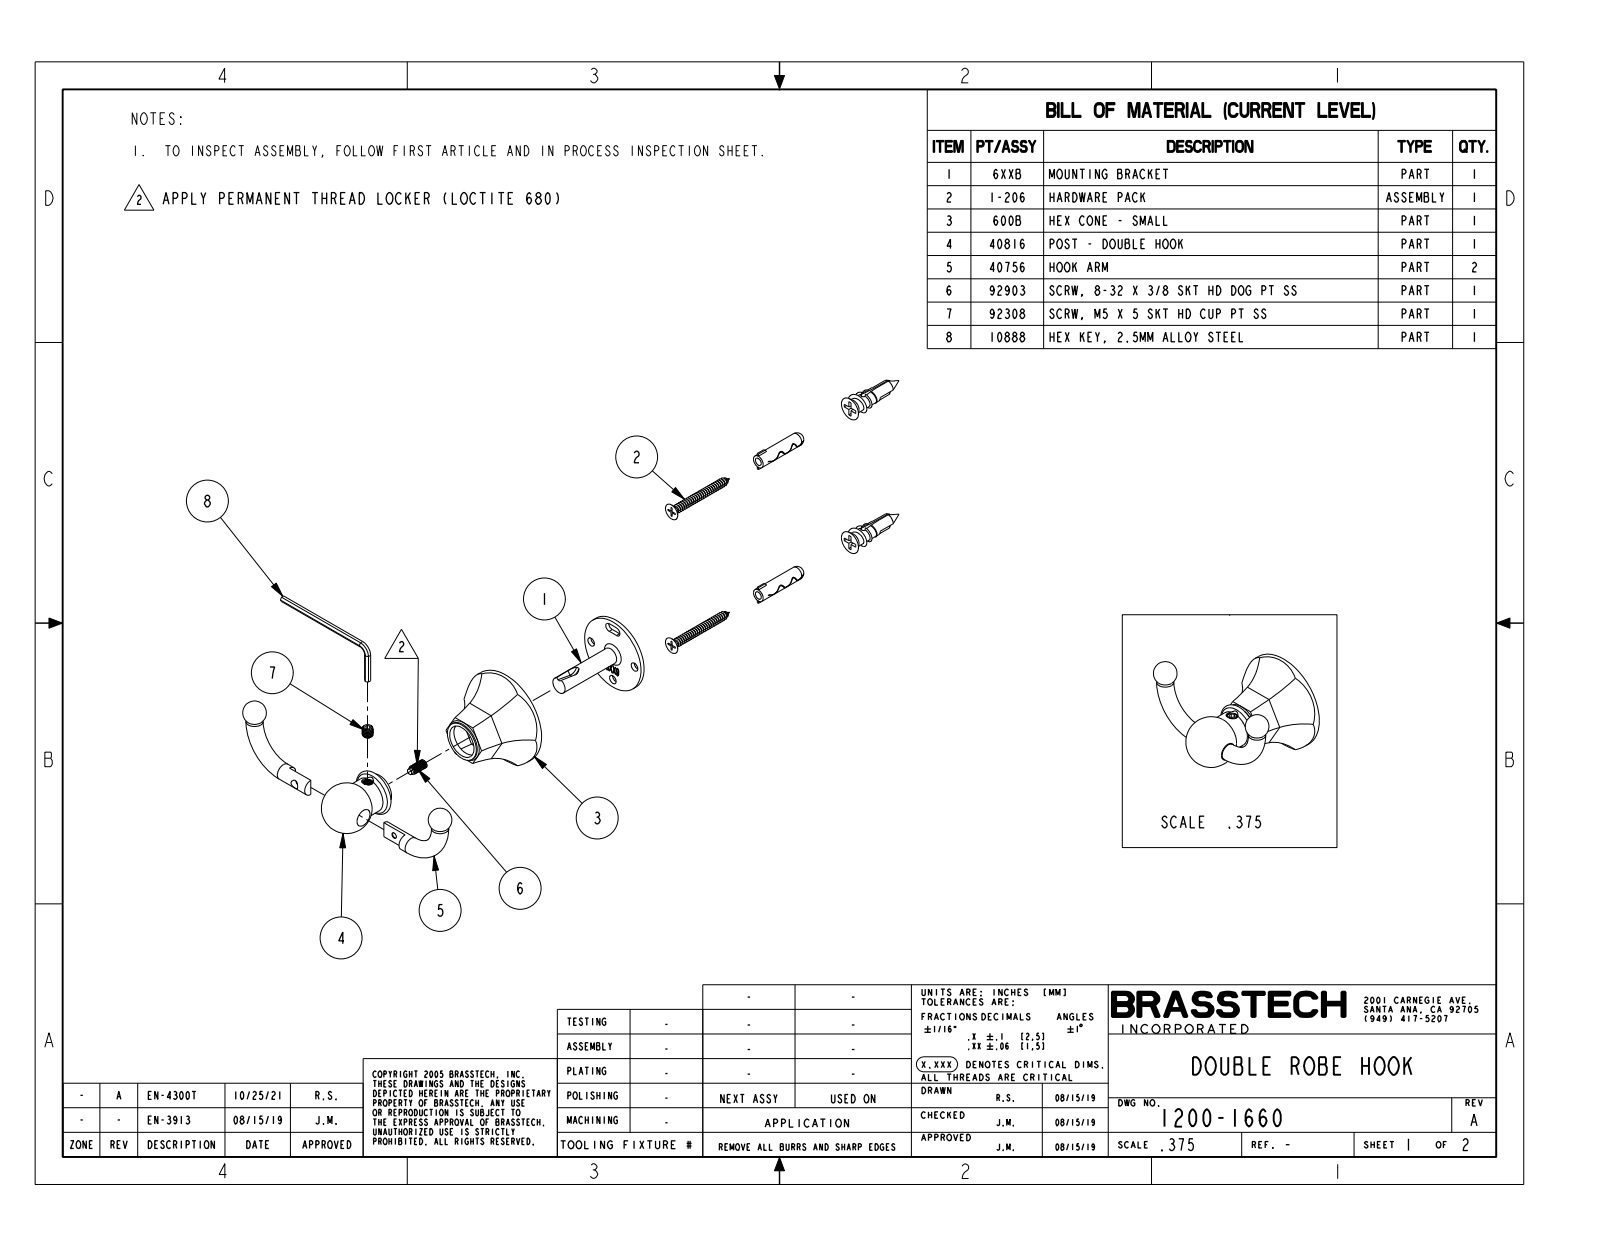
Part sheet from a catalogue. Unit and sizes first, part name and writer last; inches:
Units: inches
Overall size (bounding box): 2.814 × 2.344 × 2.087
Round bosses / shafts (diameter × count): ⌀0.315 ×3, ⌀1.85 ×1, ⌀0.748 ×1, ⌀0.68 ×1
Partial cylindrical surfaces — rounded edges, fillets, slot ends (radius × count): R0.977 ×6, R3.462 ×6
Main face-to-face distances: 1.091, 1.142, 0.051
Volume: 2.202 in³ · Surface area: 14.67 in²
Bodies: 1 solid, 45 faces (3 planar, 26 cylindrical, 16 other)
Part name (STEP PRODUCT): 1200-1660
STEP written by: CREO PARAMETRIC BY PTC INC, 2018400 (CONFIG_CONTROL_DESIGN)
